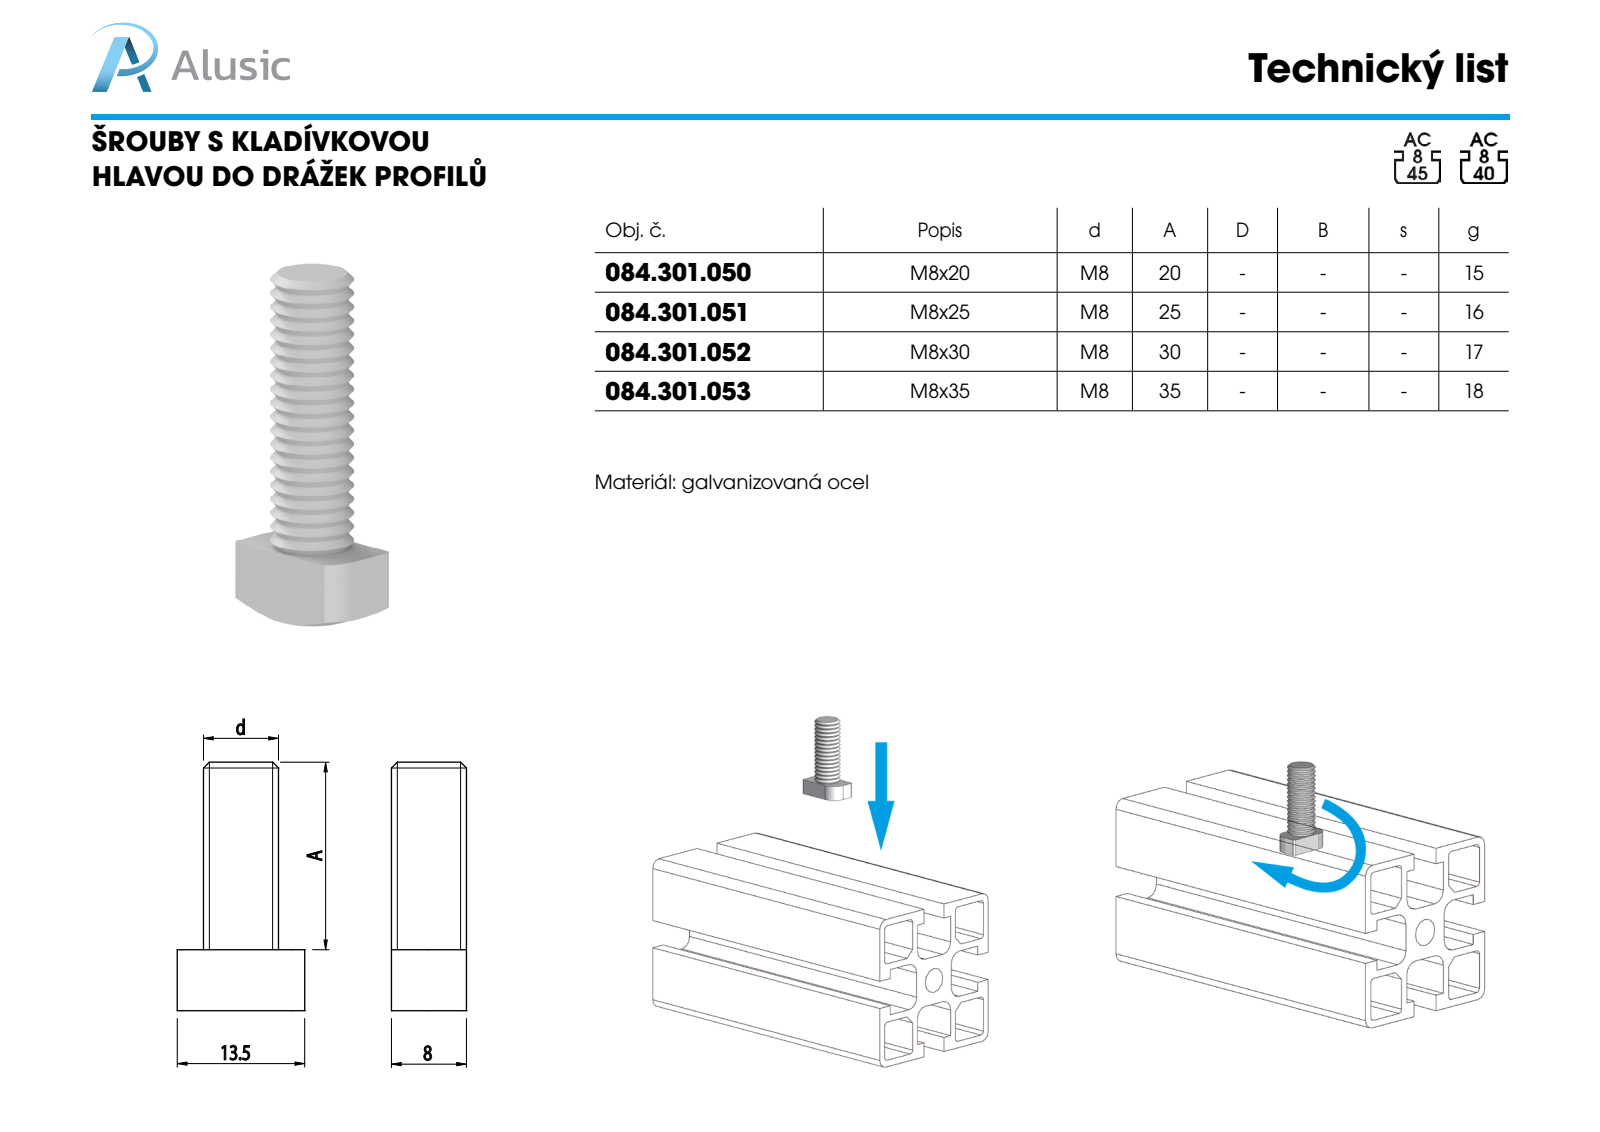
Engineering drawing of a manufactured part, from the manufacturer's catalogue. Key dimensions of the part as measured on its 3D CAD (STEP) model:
Part name (STEP PRODUCT): 084.301.053
STEP written by: SolidWorks 2012 (CONFIG_CONTROL_DESIGN)
Units: millimetres
Bodies: 1 solid, 123 faces (7 planar, 4 cylindrical, 112 other)
Overall size (bounding box): 41.5 × 13.6 × 8
Volume: 2 183 mm³ · Surface area: 1 622 mm²
Partial cylindrical surfaces — rounded edges, fillets, slot ends (radius × count): R0.5 ×2, R6.75 ×2
Main face-to-face distances: 8, 6.5, 35, 41.5, 13.6
